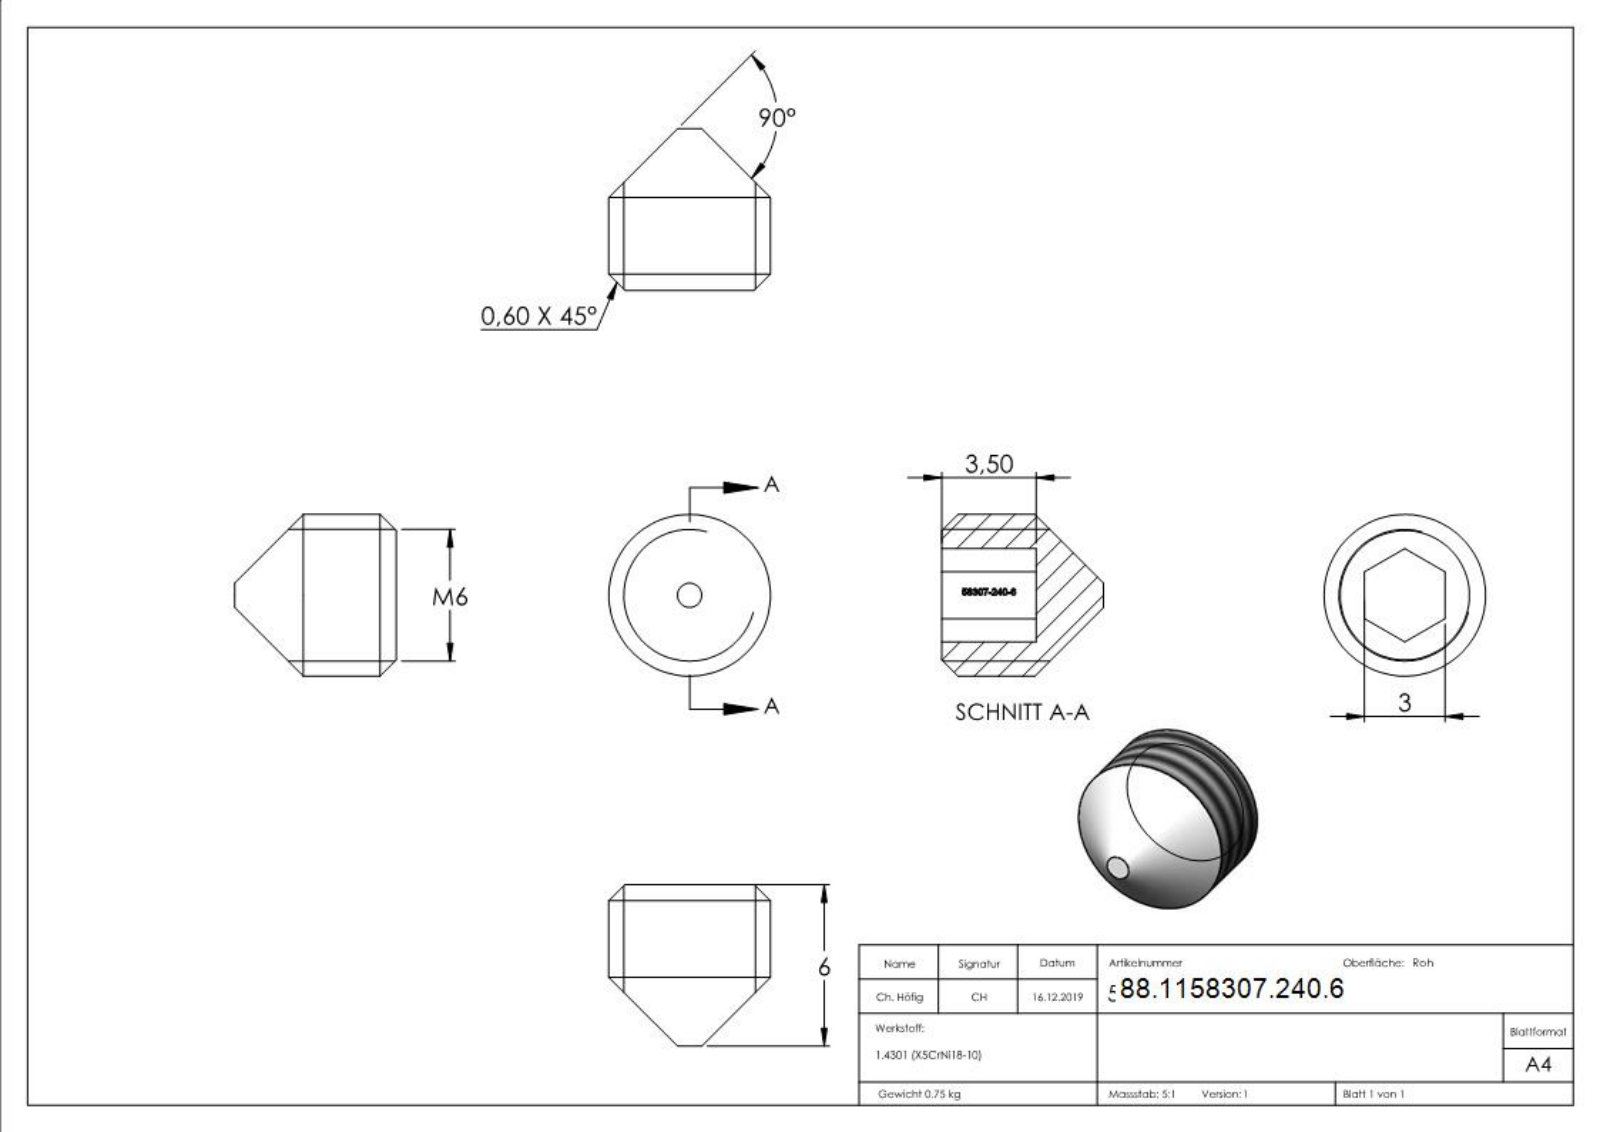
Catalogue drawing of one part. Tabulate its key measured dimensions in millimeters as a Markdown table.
| quantity | value |
| --- | --- |
| part name | 58307-240-6 |
| STEP written by | SolidWorks 2015 (CONFIG_CONTROL_DESIGN) |
| units | millimeters |
| bodies | 1 solid, 157 faces (68 planar, 1 cylindrical, 88 other) |
| overall size | 70 × 6 × 6 |
| volume | 95 mm³ |
| surface area | 163 mm² |
| round bosses / shafts (diameter × count) | 6 × 1 |
| main face-to-face distances | 3, 3.5, 2.5, 6, 3.1, 3.81, 1.31, 2.19, 3.84, 1.34 |
